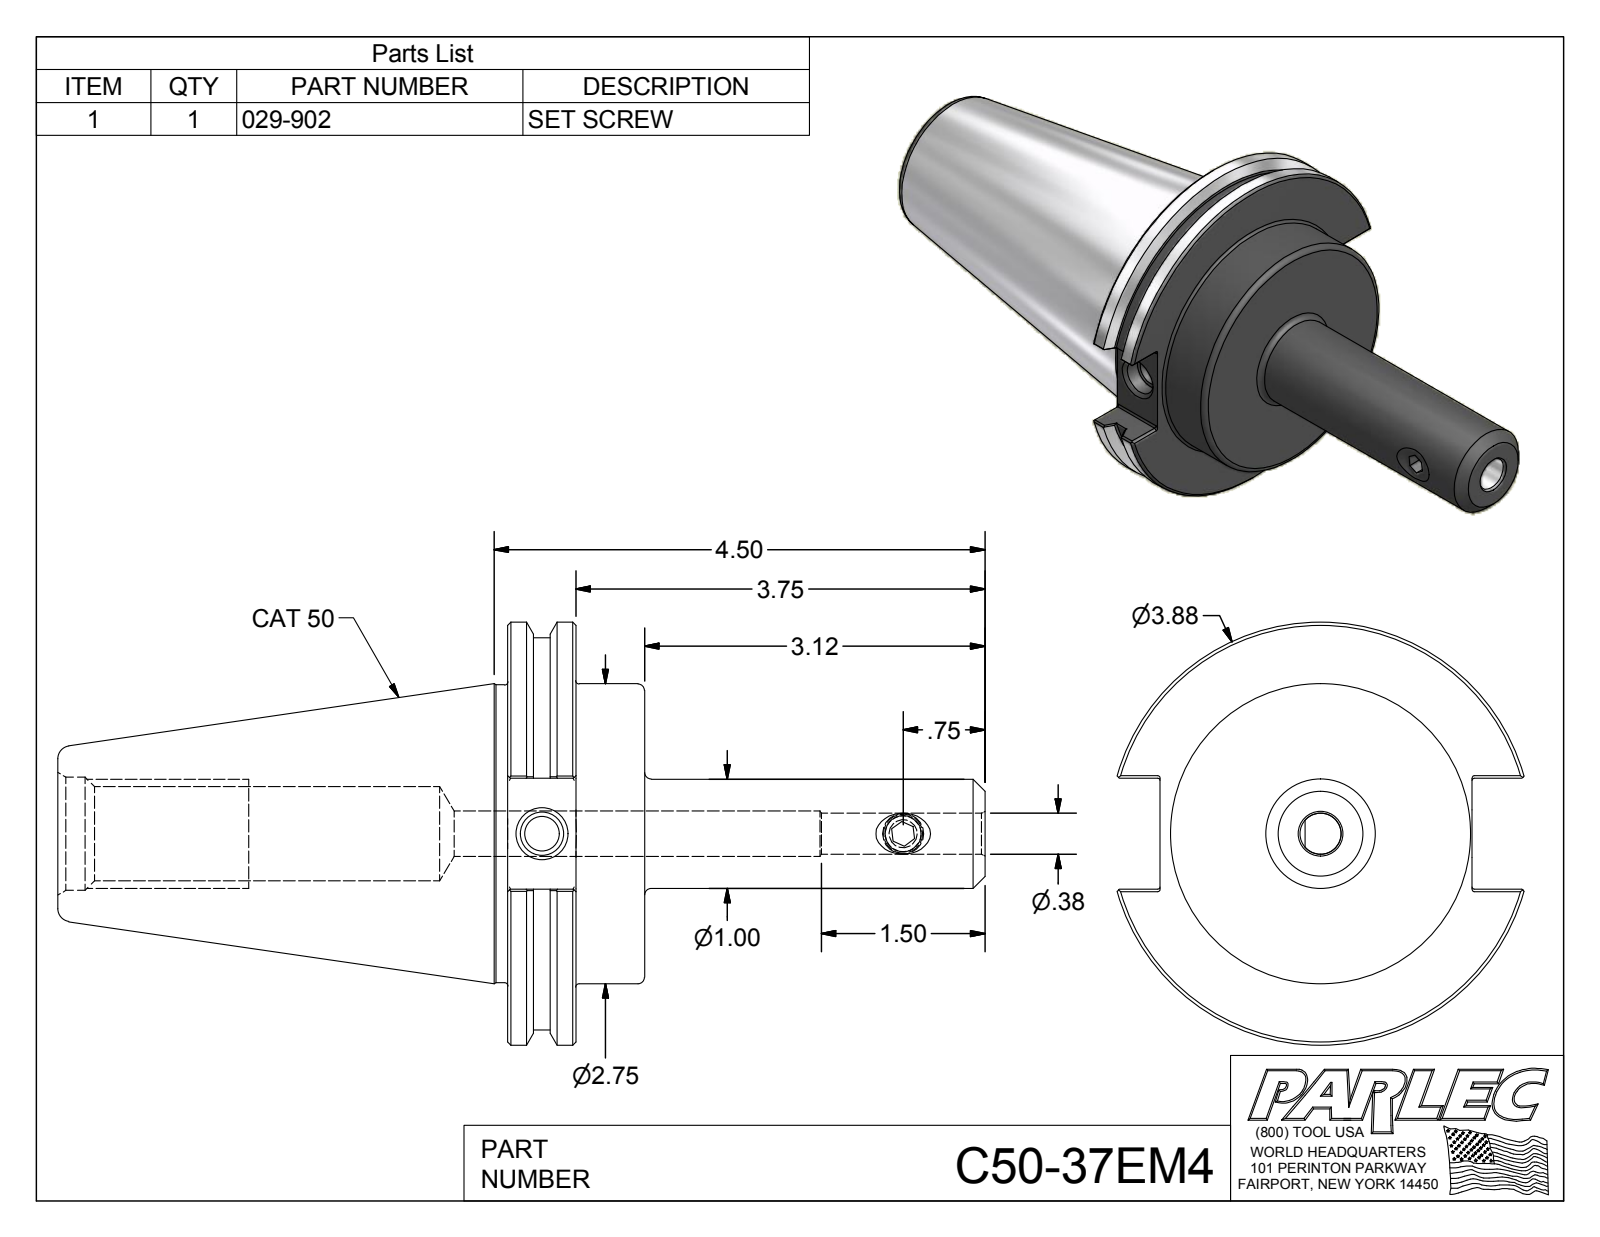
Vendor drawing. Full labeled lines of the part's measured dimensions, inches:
Part name (STEP PRODUCT): C50-37EM4; C50-37EM4-1; 029-902
STEP written by: Autodesk Inventor 2012 (AUTOMOTIVE_DESIGN)
Units: inches
Bodies: 2 solids, 104 faces (41 planar, 29 cylindrical, 34 other)
Overall size (bounding box): 8.5 × 3.875 × 3.729
Volume: 25.6 in³ · Surface area: 87.27 in²
Round holes (diameter × count): ⌀0.315 ×1, ⌀0.33 ×1, ⌀0.375 ×1, ⌀0.399 ×1, ⌀0.417 ×1, ⌀0.865 ×1, ⌀1.038 ×1
Round bosses / shafts (diameter × count): ⌀3.875 ×1, ⌀3.594 ×1, ⌀2.75 ×1, ⌀2.73 ×1, ⌀1 ×1, ⌀0.375 ×1
Partial cylindrical surfaces — rounded edges, fillets, slot ends (radius × count): R0.02 ×12
Main face-to-face distances: 1.255, 0.625, 0.63, 4.125, 4.75, 5.38, 1.015, 2.86, 8.5, 4.375
Hole centre spacings: 3.31
